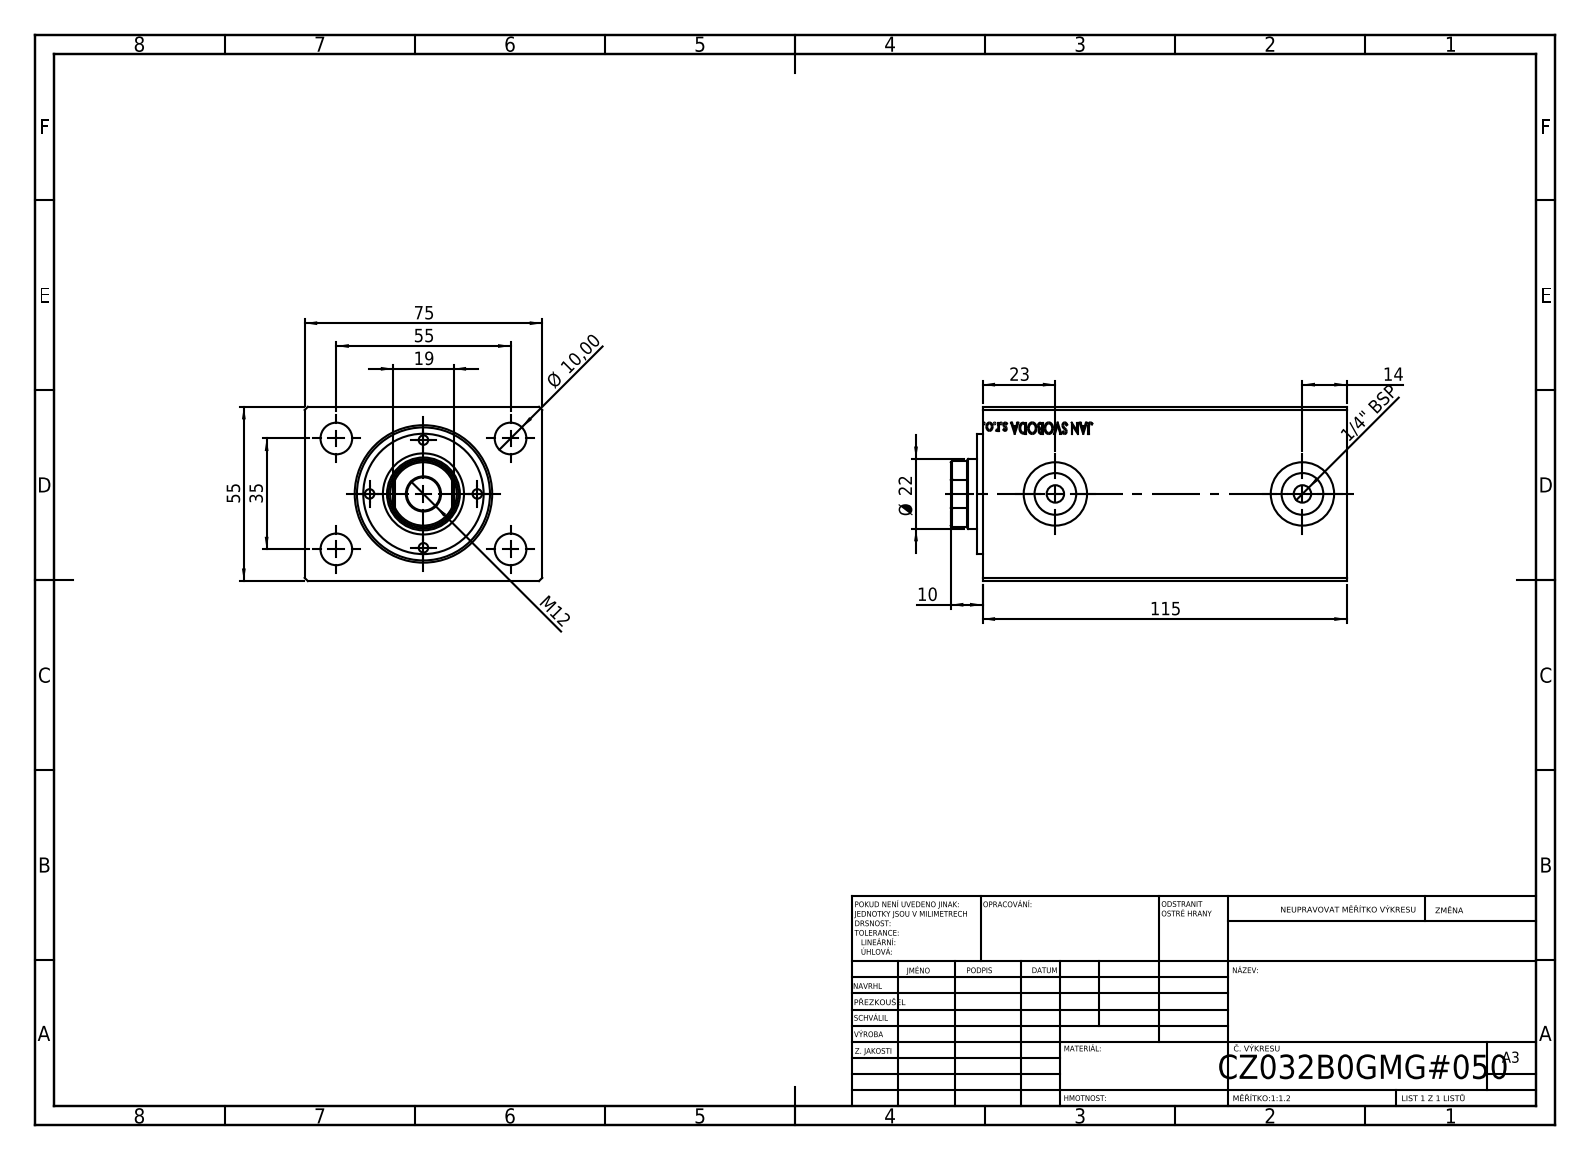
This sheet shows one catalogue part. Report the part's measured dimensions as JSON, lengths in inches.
{"part_name": "V500CZ_B_VC; V500CZ", "step_written_by": "SolidWorks 2019 (CONFIG_CONTROL_DESIGN)", "units": "inches", "bodies": {"solids": 3, "faces": 874, "planar": 400, "cylindrical": 58, "other": 416}, "overall_size": [4.921, 2.953, 2.165], "volume_in3": 26.49, "surface_area_in2": 110.4, "round_holes": [[0.118, 4], [0.394, 4], [0.217, 2], [0.518, 2], [0.787, 2], [0.413, 1], [0.866, 1], [0.906, 1], [1.26, 1], [1.417, 1], [1.654, 1]], "round_bosses_or_shafts": [[1.496, 1]], "partial_cylinders_radius": [[0.413, 1]], "face_to_face_distances": [2.165, 2.953, 4.528, 3.984, 0.543, 0.394, 0.323, 0.071, 4.52, 0.535], "hole_center_spacings": [0.669, 0.804, 0.946, 1.083, 1.283, 1.737, 1.883, 1.339]}
